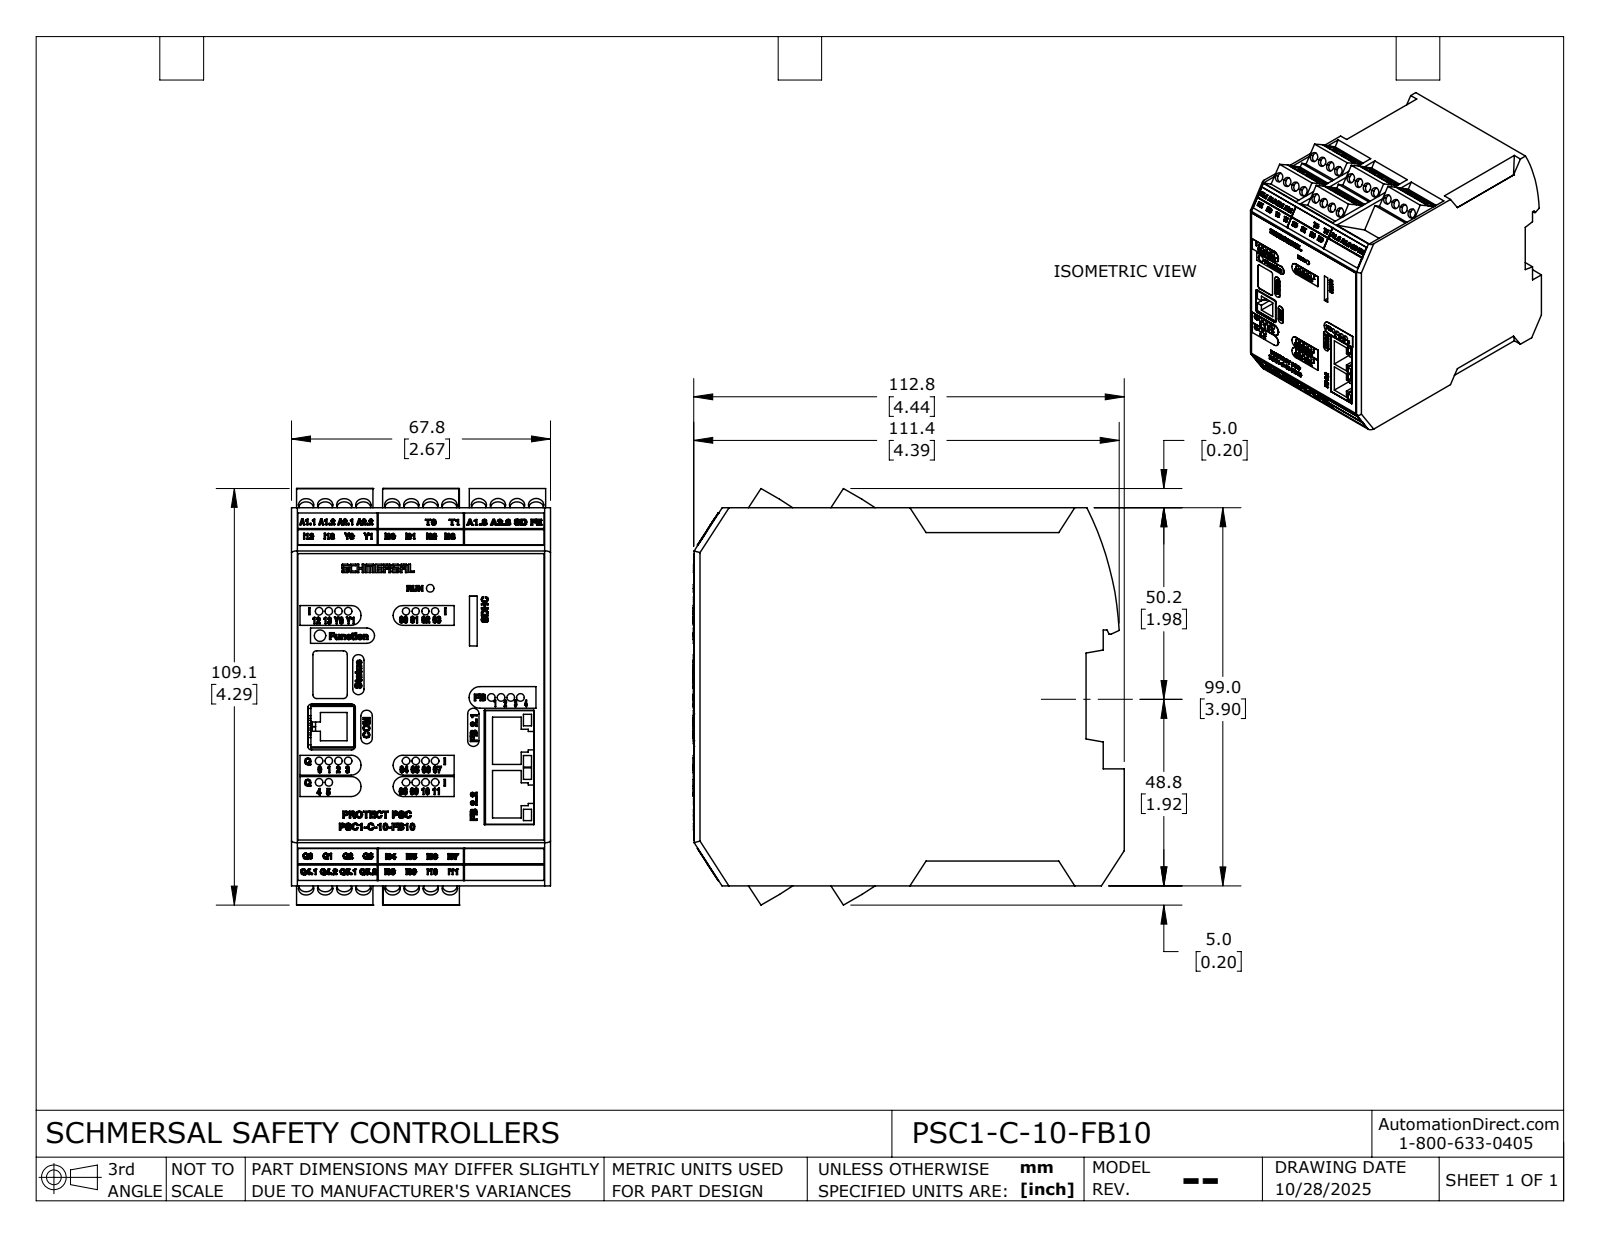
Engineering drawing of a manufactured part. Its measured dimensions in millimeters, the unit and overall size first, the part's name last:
Units: millimetres
Overall size (bounding box): 112.9 × 109.09 × 67.8
Round holes (diameter × count): ⌀4 ×36, ⌀2 ×22, ⌀1.89 ×4, ⌀3 ×1
Round bosses / shafts (diameter × count): ⌀1 ×2, ⌀2 ×1
Partial cylindrical surfaces — rounded edges, fillets, slot ends (radius × count): R1.5 ×14, R1 ×9, R0.3 ×8, R0.4 ×6, R2.6 ×6, R0.45 ×4, R0.7 ×4, R0.2 ×2
Main face-to-face distances: 67.8, 99, 102.75, 10, 22.6, 20.1, 112.75, 18.1, 11.77, 20
Hole centre spacings: 5, 2.54, 10, 11.76, 5.08, 12.78, 39.28, 22.78
Volume: 704 169 mm³ · Surface area: 62 323 mm²
Bodies: 1 solid, 4447 faces (2081 planar, 227 cylindrical, 2139 other)
Part name (STEP PRODUCT): PSC1-C-10-FB10
STEP written by: SolidWorks 2024 (AUTOMOTIVE_DESIGN)
